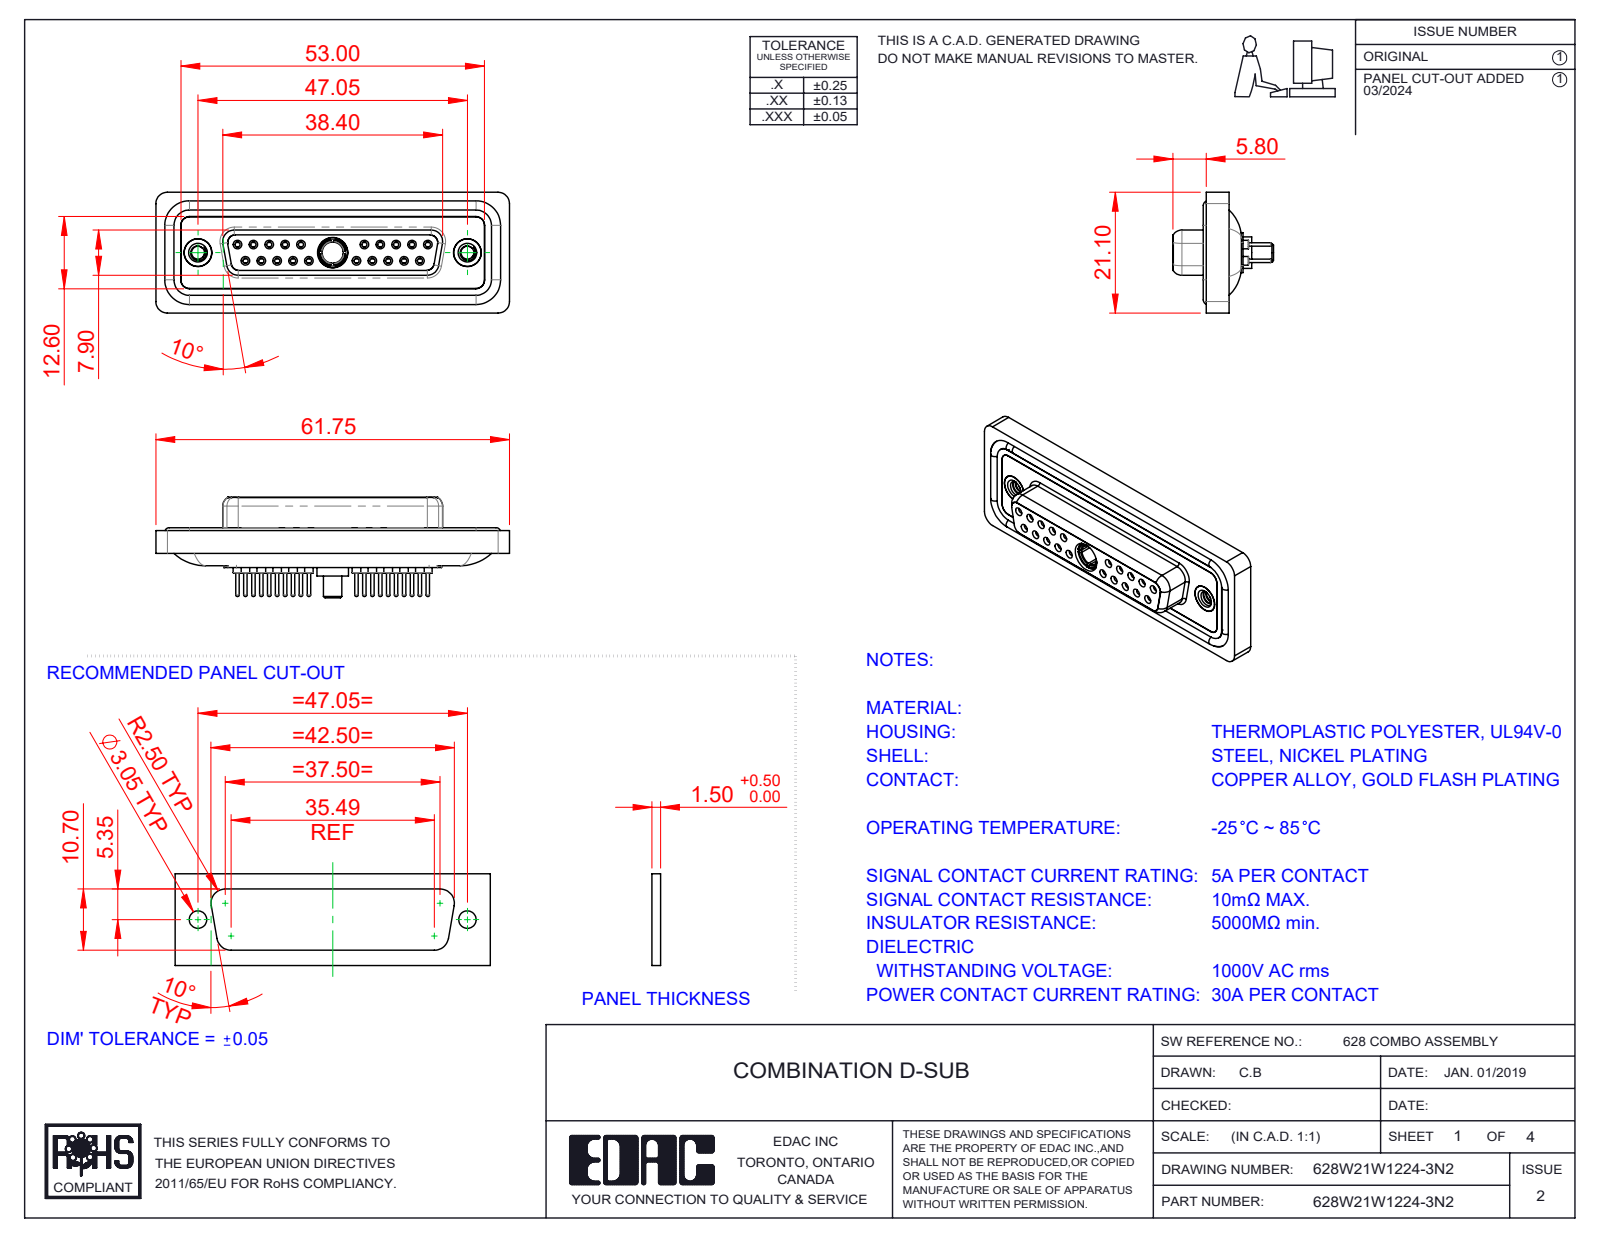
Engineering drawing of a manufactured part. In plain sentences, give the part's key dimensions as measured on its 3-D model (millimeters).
The part is named "Power Socket_30A S; 628Combo Shell Rear_25 Contacts; 628Combo Housing_21W1; 628W21W1224-3N2 (+5 more)". Its 3-D file was written by "SolidWorks 2023 (CONFIG_CONTROL_DESIGN)". It is 29 solids with 1560 faces: 434 planar, 591 cylindrical and 535 other. Overall it measures 61.75 by 21.1 by 17.55 millimeters. Its volume is 8 381 cubic millimeters and its surface area 14 006 square millimeters. Round holes: 20 of diameter 0.9, 20 of diameter 1.1, 20 of diameter 1.5, 20 of diameter 2, 10 of diameter 1.6, 10 of diameter 1.7, 3 of diameter 4.85, 2 of diameter 2.26, 2 of diameter 4, 2 of diameter 4.05, 2 of diameter 5, 1 of diameter 3.7. Round bosses or shafts: 20 of diameter 2.2, 20 of diameter 0.6, 14 of diameter 1.6, 2 of diameter 4.95, 2 of diameter 4.8, 1 of diameter 5.5, 1 of diameter 5.2, 1 of diameter 4.96. Partial cylindrical surfaces (rounded edges, fillets, slot ends): 22 of radius 1.5, 18 of radius 2, 8 of radius 1.35, 8 of radius 1.6, 4 of radius 0.25, 4 of radius 0.5, 4 of radius 0.6, 4 of radius 0.65. The main face-to-face distances are 0.4, 1.8, 7.45, 6.6, 5.65, 0.5, 1.6, 7.05, 2.9, 1.1. The hole center spacings are 3.16, 2.77, 5.54, 5.03, 8.31, 7.48, 16.62, 19.39.
